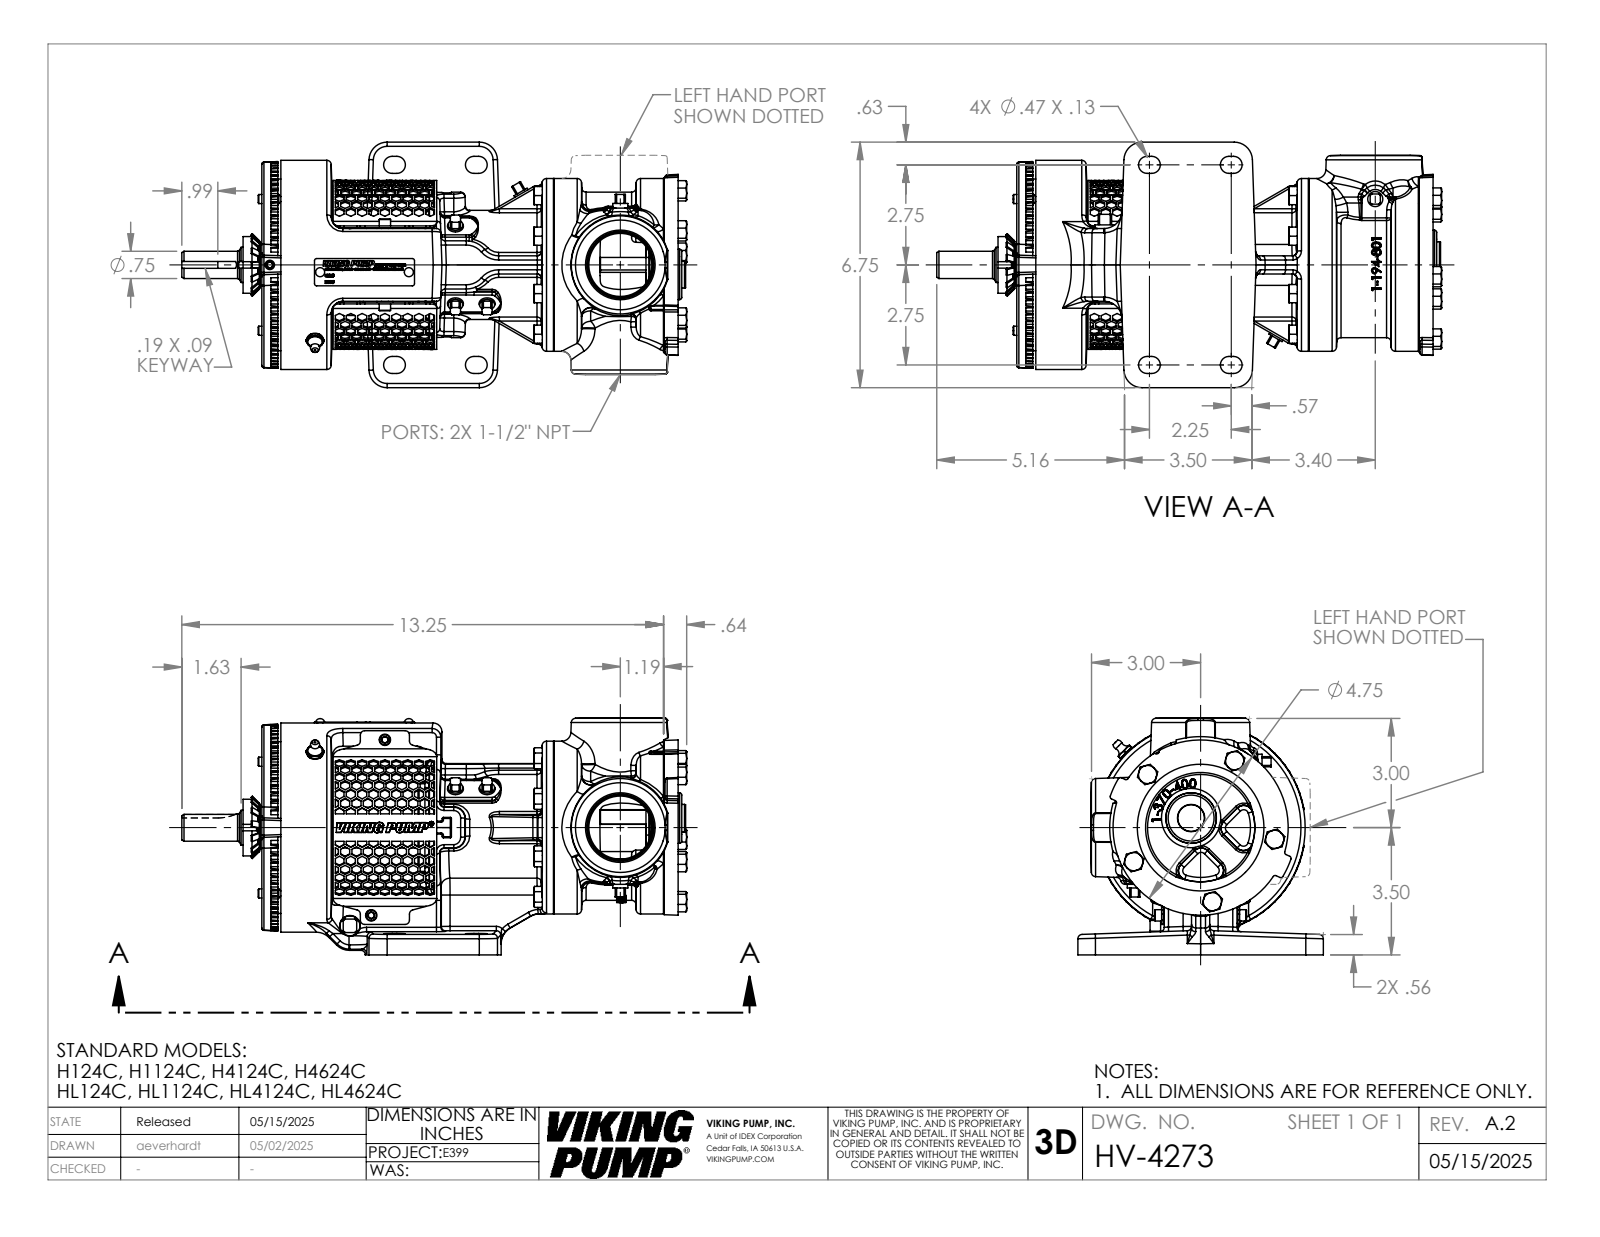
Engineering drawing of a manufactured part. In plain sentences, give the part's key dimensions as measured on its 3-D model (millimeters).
The part is named "HV-4273". Its 3-D file was written by "SolidWorks 2024 (AUTOMOTIVE_DESIGN)". It is 1 solid with 3811 faces: 1207 planar, 780 cylindrical and 1824 other. Overall it measures 352.7 by 171.5 by 165.5 millimeters. Its volume is 2 733 000 cubic millimeters and its surface area 316 100 square millimeters. Round holes: 6 of diameter 6.4, 3 of diameter 4, 3 of diameter 5, 2 of diameter 6.5, 1 of diameter 25, 1 of diameter 25.1, 1 of diameter 32.1, 1 of diameter 32.3, 1 of diameter 46.5, 1 of diameter 114.4. Round bosses or shafts: 3 of diameter 11.1, 3 of diameter 7.9, 2 of diameter 6.4, 1 of diameter 146.1, 1 of diameter 120.7, 1 of diameter 120.6, 1 of diameter 114.3, 1 of diameter 101.6. Partial cylindrical surfaces (rounded edges, fillets, slot ends): 140 of radius 1.4, 99 of radius 3, 44 of radius 1.5, 22 of radius 0.8, 20 of radius 12.7, 11 of radius 6.1, 10 of radius 6.4, 8 of radius 5.9. The main face-to-face distances are 49.3, 290.8, 241.5, 13.3, 36, 277.5, 11.2, 2.1, 38.1, 279.6. The hole center spacings are 65, 112.6, 35.6, 52.5, 62.9, 130, 20.6, 45.5.
